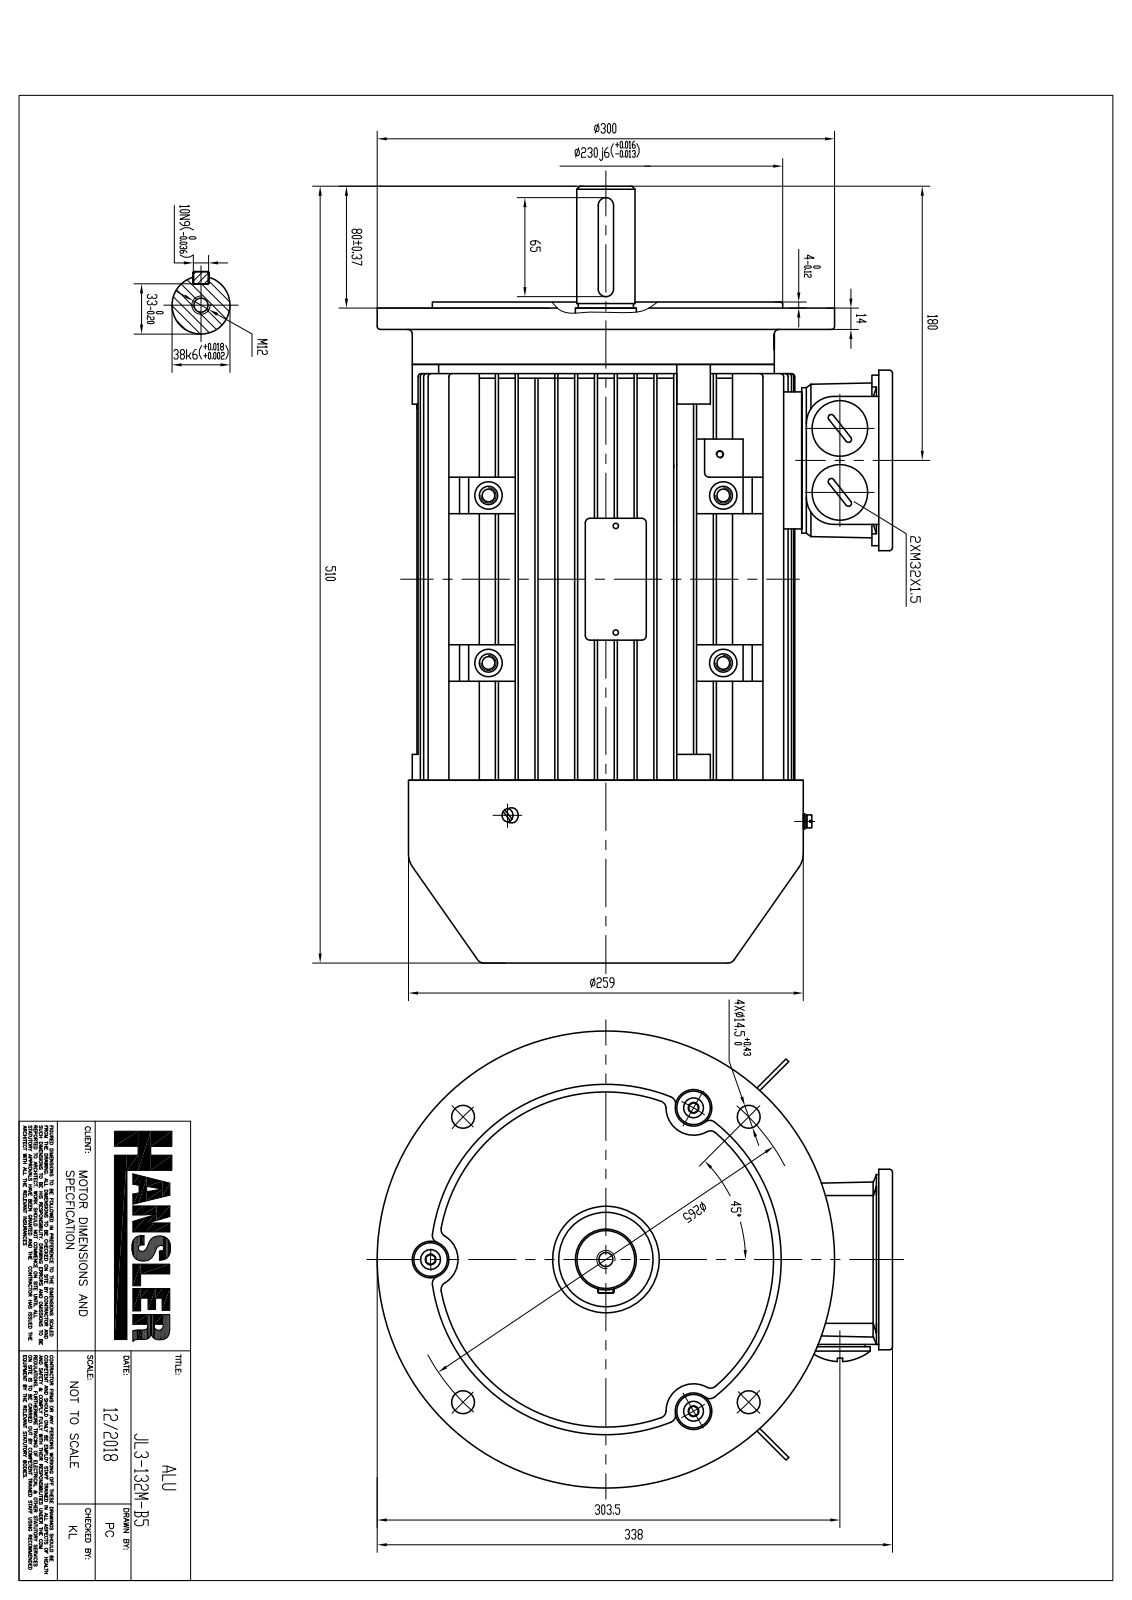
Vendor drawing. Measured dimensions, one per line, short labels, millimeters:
name: JL3-132M-B5
written by: SolidWorks 2018 (CONFIG_CONTROL_DESIGN)
unit: mm
bodies: 47 solids, 4783 faces (2112 planar, 2077 cylindrical, 594 other)
size: 496 × 337.82 × 300
volume: 3 663 000 mm³; area: 1 755 000 mm²
holes: 27× ⌀5, 14× ⌀10, 12× ⌀2.92, 8× ⌀18, 6× ⌀5.8, 5× ⌀5.25, 5× ⌀5.3, 4× ⌀2.98, 4× ⌀5.5, 4× ⌀8, 4× ⌀8.5, 4× ⌀15
bosses: 16× ⌀3.82, 9× ⌀10, 8× ⌀12, 6× ⌀5.5, 5× ⌀7.85, 5× ⌀4.48, 4× ⌀16, 4× ⌀5
rounds: 816× R0.5, 62× R2, 52× R3, 52× R5, 36× R1, 26× R4, 18× R2.5, 12× R0.2
face distances: 13, 2, 26, 11, 91, 15, 104, 78, 39, 28
hole spacings: 68, 84.34, 10.4, 21.21, 96.17, 117.38, 144.72, 7.23
